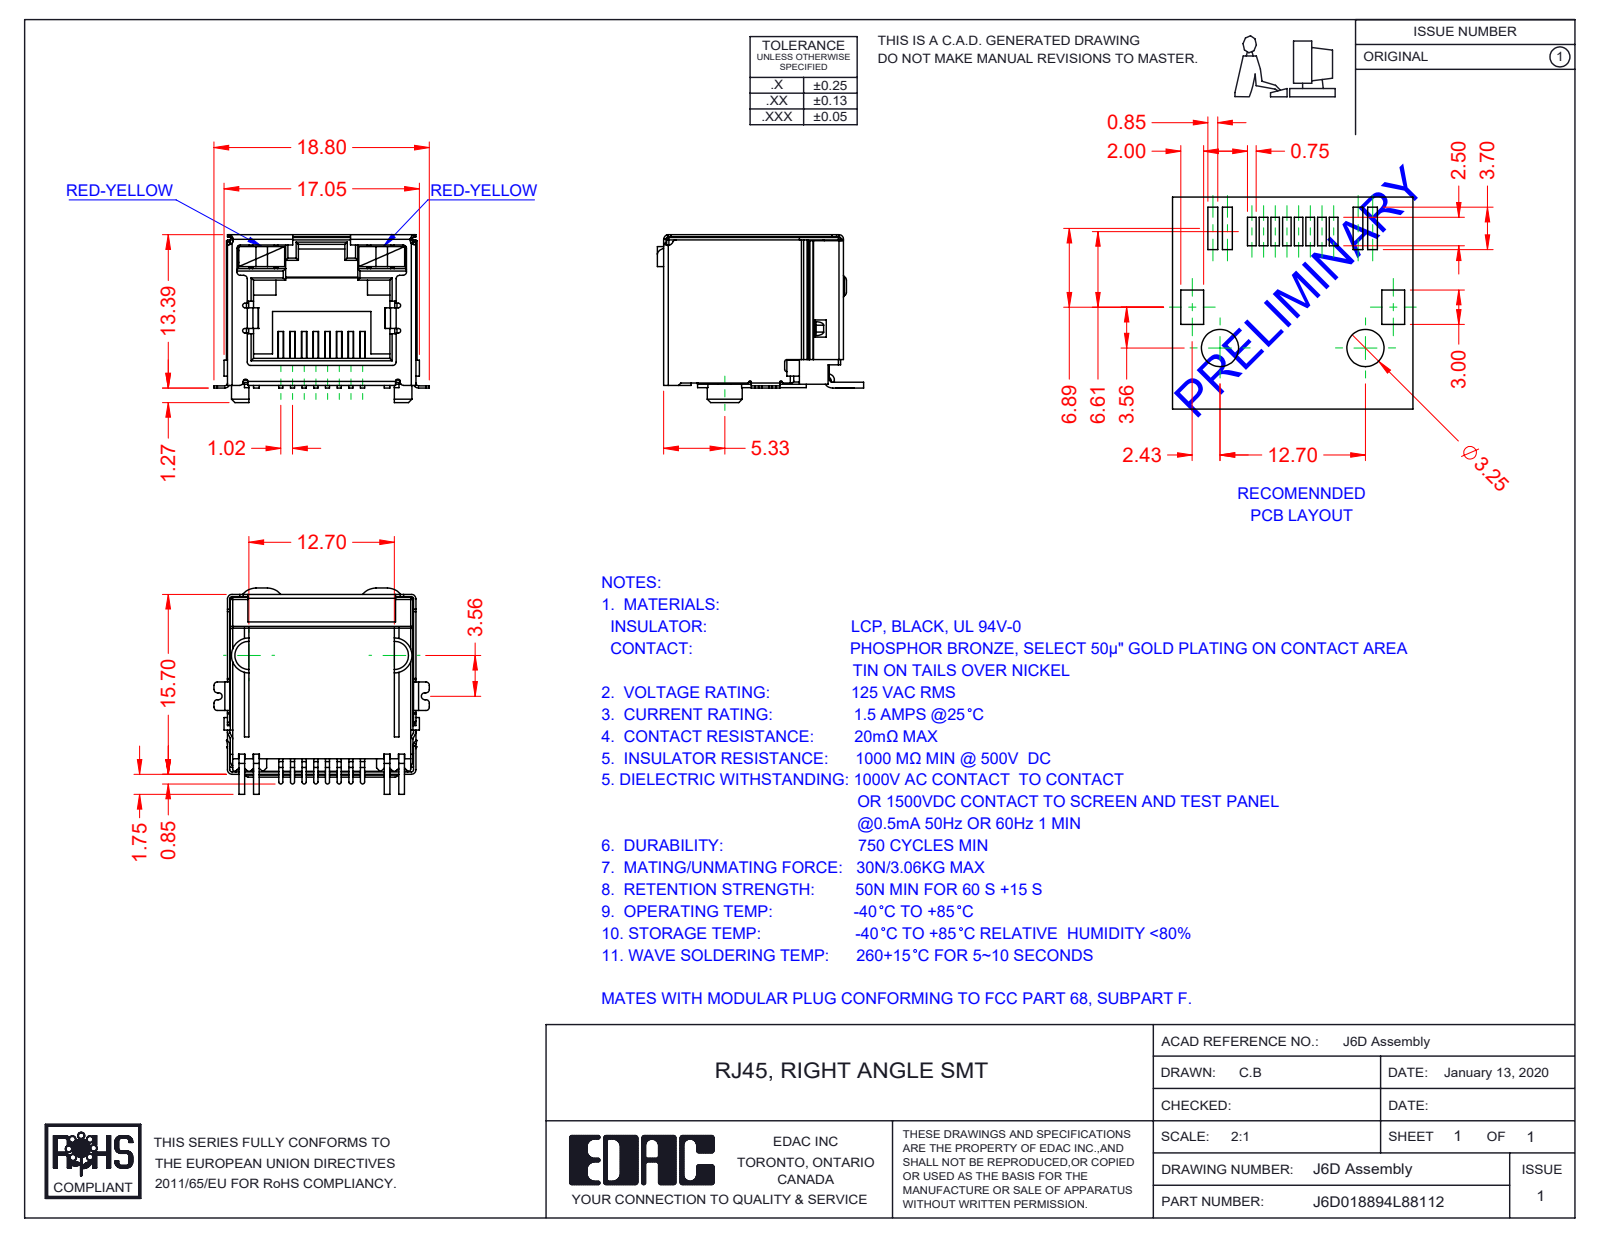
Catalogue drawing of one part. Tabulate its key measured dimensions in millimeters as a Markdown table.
| quantity | value |
| --- | --- |
| part name | 6D Shield_LED - No EMI; 6D LED LH_8-Red-Yellow; 6D LED RH_8-Red-Yellow; 6D Insulator (+2 more) |
| STEP written by | SolidWorks 2016 (CONFIG_CONTROL_DESIGN) |
| units | millimeters |
| bodies | 12 solids, 899 faces (646 planar, 220 cylindrical, 33 other) |
| overall size | 18.8 × 18 × 14.65 |
| volume | 1 804 mm³ |
| surface area | 4 898 mm² |
| partial cylindrical surfaces (radius × count) | 0.3 × 39, 0.2 × 37, 0.4 × 16, 0.1 × 12, 0.15 × 8, 0.18 × 8, 0.5 × 6, 1.5 × 5 |
| main face-to-face distances | 16, 16.25, 16.2, 2.25, 1, 15.95, 16.05, 12.8, 0.45, 16.45 |
